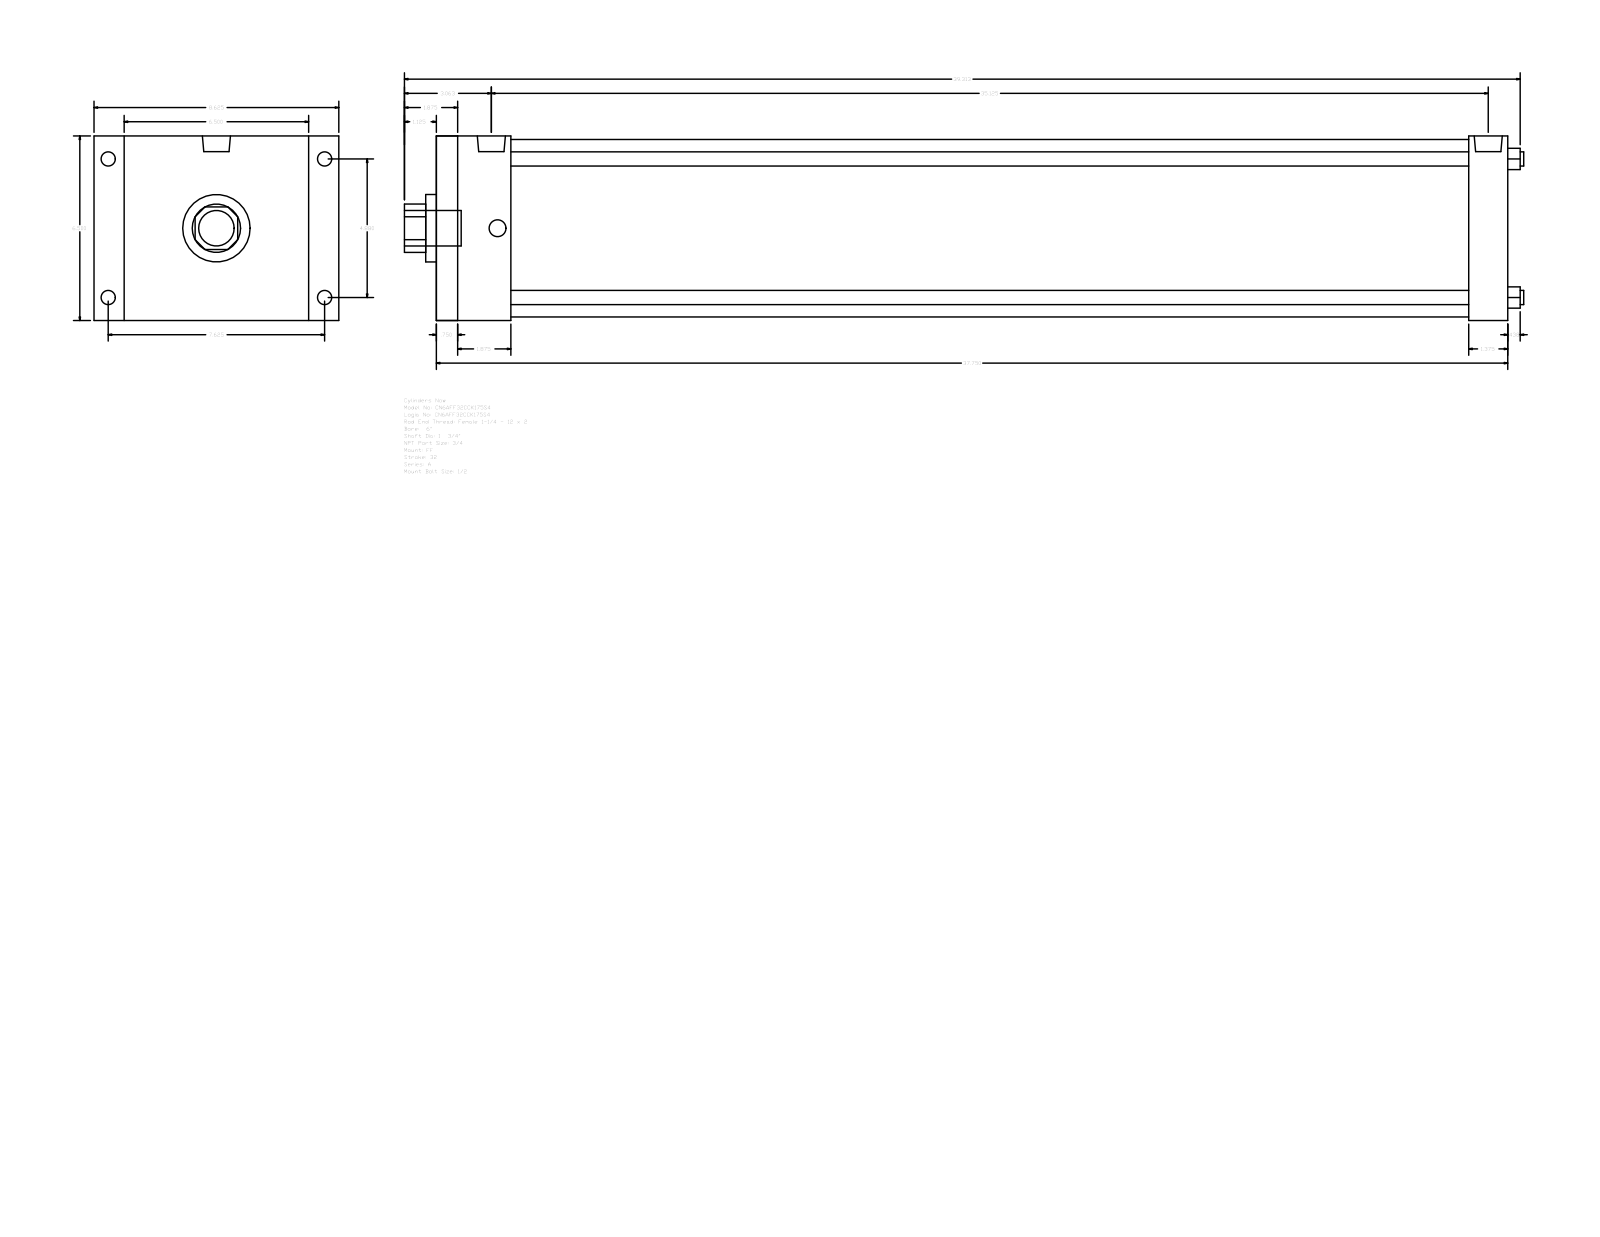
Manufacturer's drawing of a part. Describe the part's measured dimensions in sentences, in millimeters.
The part is named "A_FF__0600_1.75". Its 3-D file was written by "GSSL Pune (CONFIG_CONTROL_DESIGN)". It is 0 solids with 92 faces: 64 planar, 28 cylindrical and 0 other. Overall it measures 1001.71 by 219.07 by 165.1 millimeters. Round holes: 4 of diameter 12.7, 1 of diameter 44.45, 1 of diameter 60.33, 1 of diameter 158.75. Round bosses or shafts: 4 of diameter 15.08, 4 of diameter 12.7, 2 of diameter 25.12, 1 of diameter 31.75. Partial cylindrical surfaces (rounded edges, fillets, slot ends): 1 of radius 21.63. The main face-to-face distances are 165.1, 958.85, 19.05, 939.8, 34.92, 66.68, 47.63, 892.17, 923.93, 904.88. The hole center spacings are 87.65, 123.96, 175.31.
